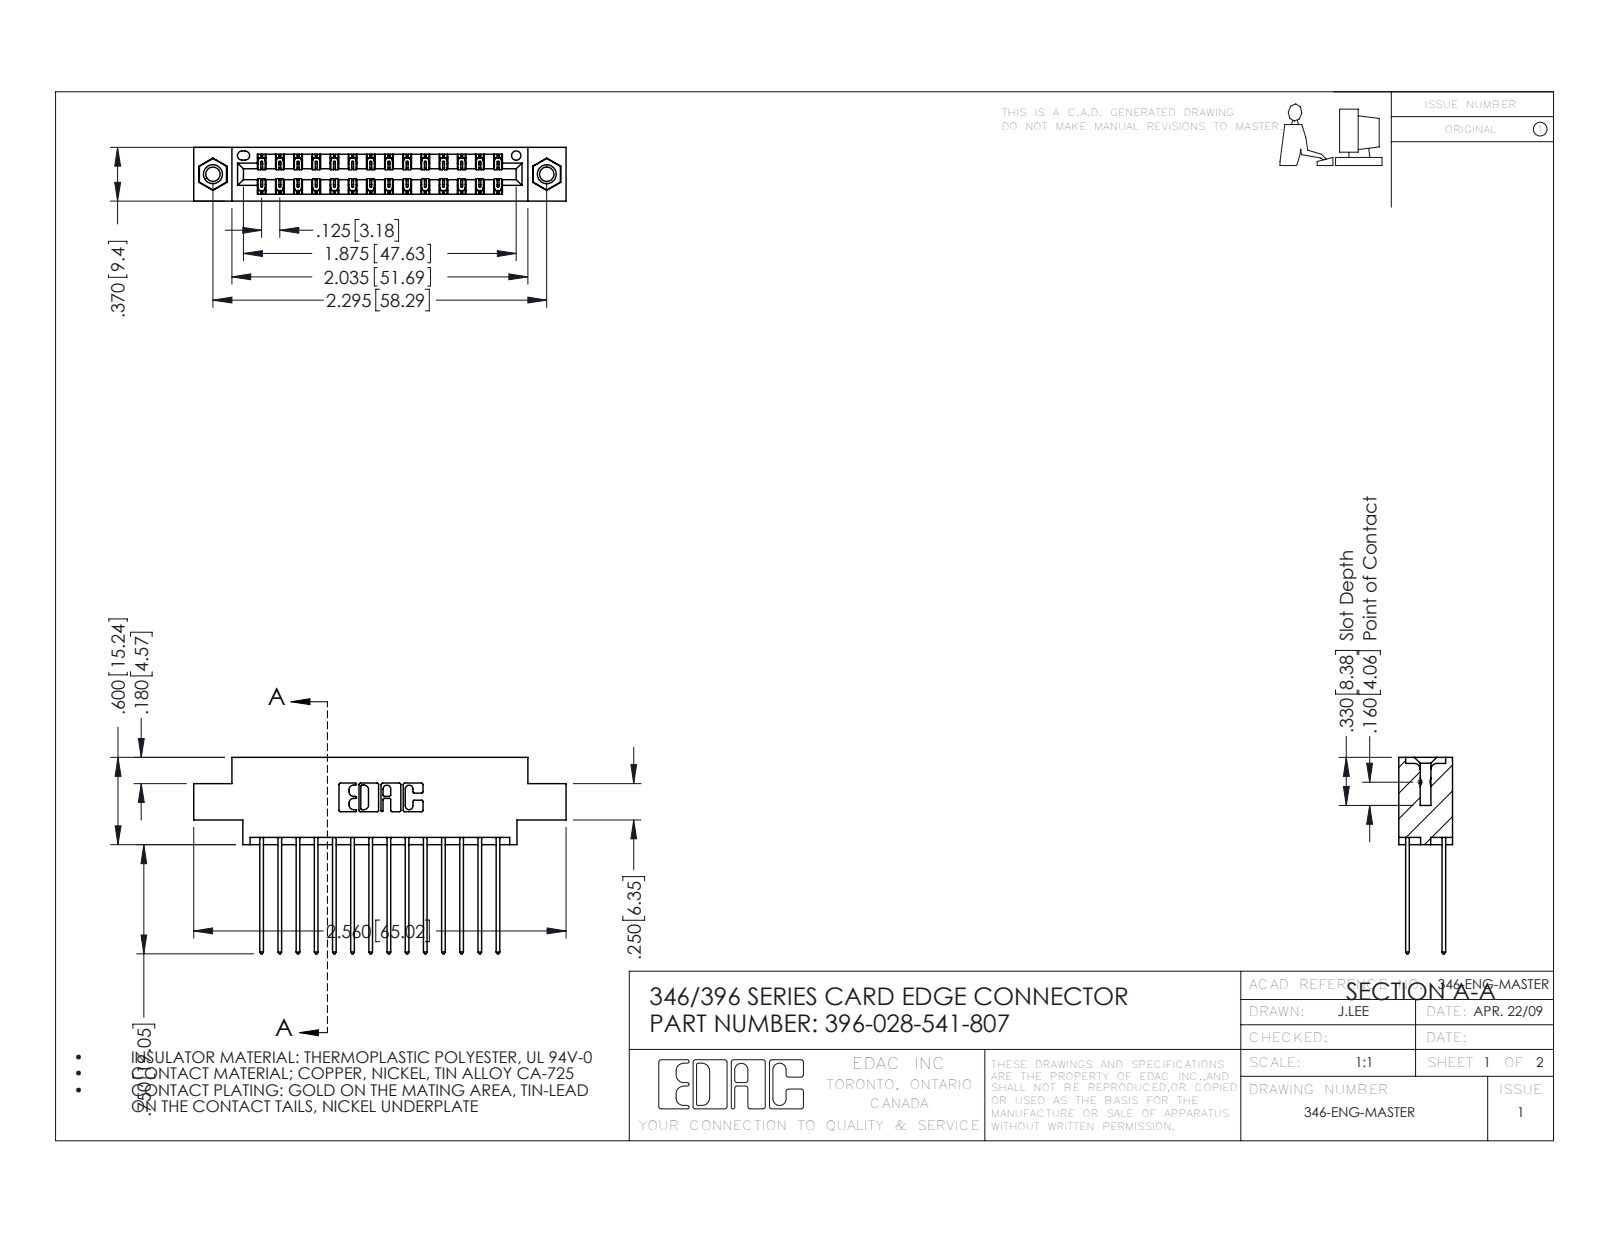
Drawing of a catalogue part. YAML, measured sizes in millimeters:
part_name: "346 Part_0.170 Offset - 0.156 Dia-TI; 345-250-001_345-250-005-103; 396-028-541-807; 345-292-001_345-293-141"
step_written_by: "SolidWorks 2016 (CONFIG_CONTROL_DESIGN)"
units: millimeters
bodies: {solids: 31, faces: 1642, planar: 1092, cylindrical: 534, other: 16}
overall_size: [65, 34.3, 9.4]
volume: 6110
surface_area: 8948
round_holes:
  - {diameter: 2.5, count: 2}
  - {diameter: 3.2, count: 2}
  - {diameter: 4, count: 2}
  - {diameter: 1.6, count: 1}
round_bosses_or_shafts:
  - {diameter: 3.9, count: 2}
partial_cylinders:
  - {radius: 0.2, count: 42}
  - {radius: 0.3, count: 28}
  - {radius: 0.3, count: 22}
  - {radius: 0.2, count: 6}
  - {radius: 0.8, count: 6}
  - {radius: 0.7, count: 3}
  - {radius: 0.4, count: 2}
  - {radius: 0.6, count: 2}
face_to_face_distances: [1.2, 8.2, 6.4, 9.4, 1.8, 7.6, 0.6, 7, 5.6, 3.8]
hole_center_spacings: [6.2, 53.1, 58.3]
